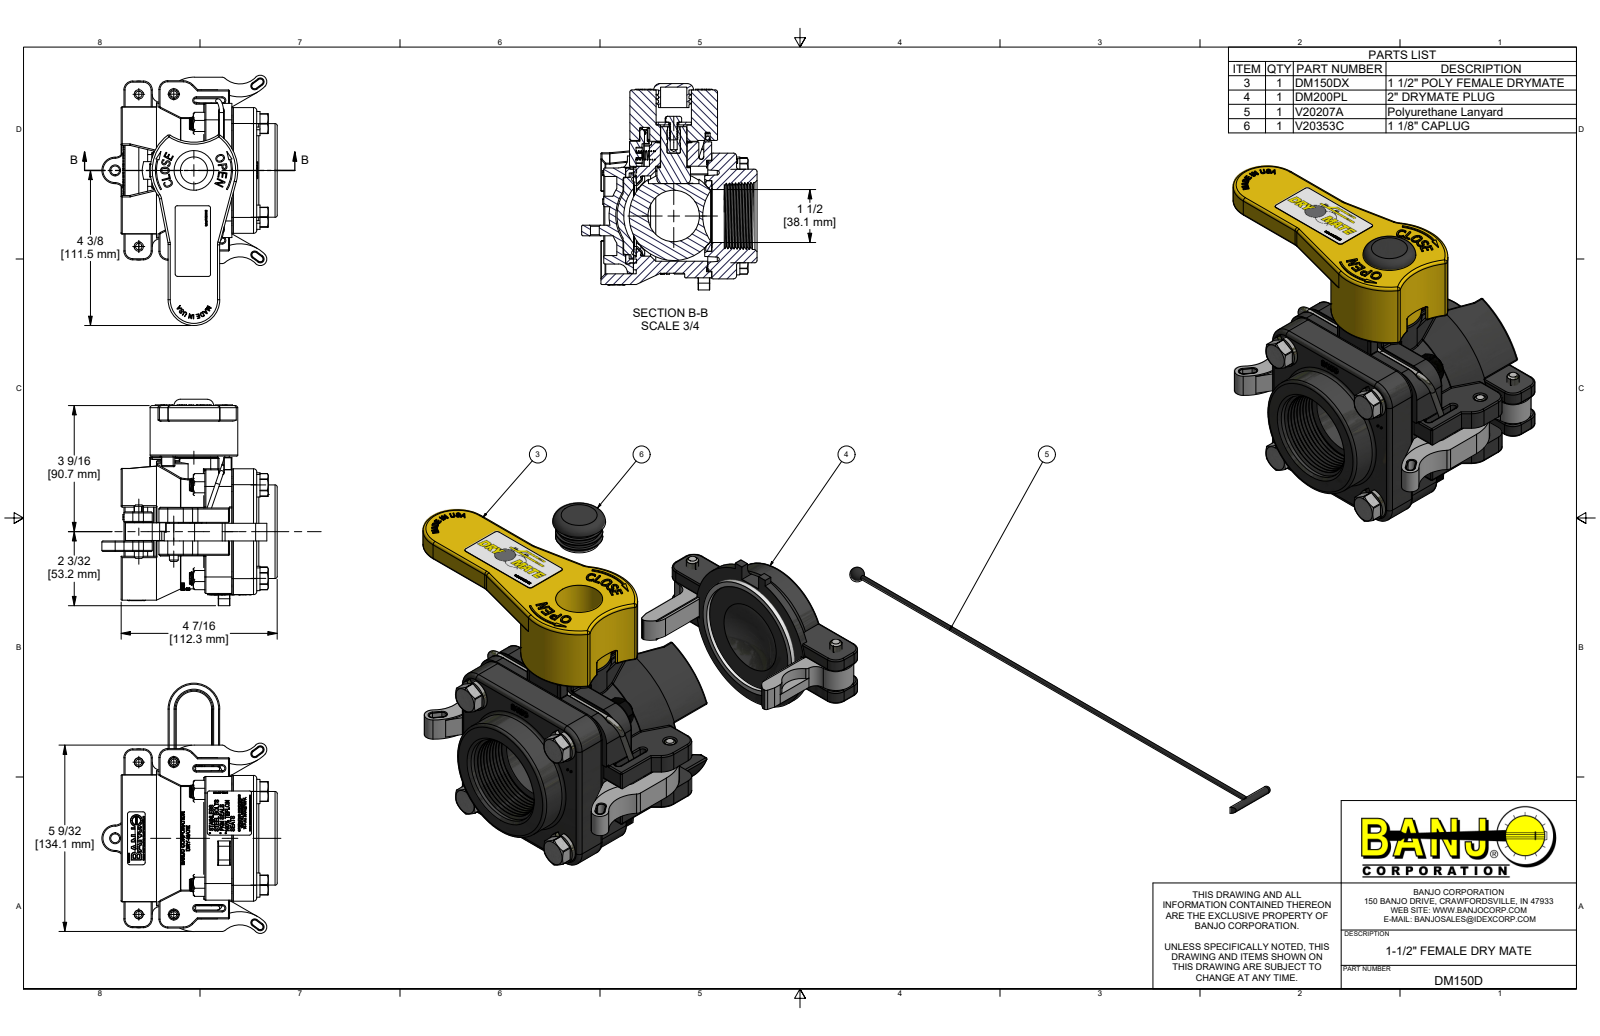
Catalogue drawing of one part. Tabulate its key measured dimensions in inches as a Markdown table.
| quantity | value |
| --- | --- |
| part name | DM150D; DM150DX; DM20254F; DM20254FY (+8 more) |
| STEP written by | Autodesk Inventor 2022 (AUTOMOTIVE_DESIGN) |
| units | inches |
| bodies | 44 solids, 6590 faces (3045 planar, 1046 cylindrical, 2499 other) |
| overall size | 7.084 × 5.845 × 4.967 |
| volume | 46.15 in³ |
| surface area | 400.5 in² |
| round holes (diameter × count) | 0.25 × 5, 0.375 × 5, 0.256 × 4, 0.307 × 4, 0.385 × 4, 0.41 × 4, 0.42 × 4, 0.125 × 3, 0.196 × 1, 0.2 × 1, 0.227 × 1, 0.281 × 1 |
| round bosses / shafts (diameter × count) | 0.324 × 60, 0.12 × 5, 0.687 × 4, 0.375 × 4, 0.26 × 4, 0.249 × 4, 0.28 × 3, 3.25 × 1 |
| partial cylindrical surfaces (radius × count) | 0.03 × 159, 0.01 × 41, 0.06 × 35, 0.02 × 20, 0.25 × 11, 0.12 × 10, 0.08 × 8, 0.09 × 8 |
| main face-to-face distances | 0.11, 0.92, 2.217, 0.298, 0.013, 2.922, 0.5, 0.08, 0.7, 3.833 |
| hole center spacings | 2.654, 1.872, 1.881, 2.648, 2.66, 3.753, 0.95, 0.986 |
